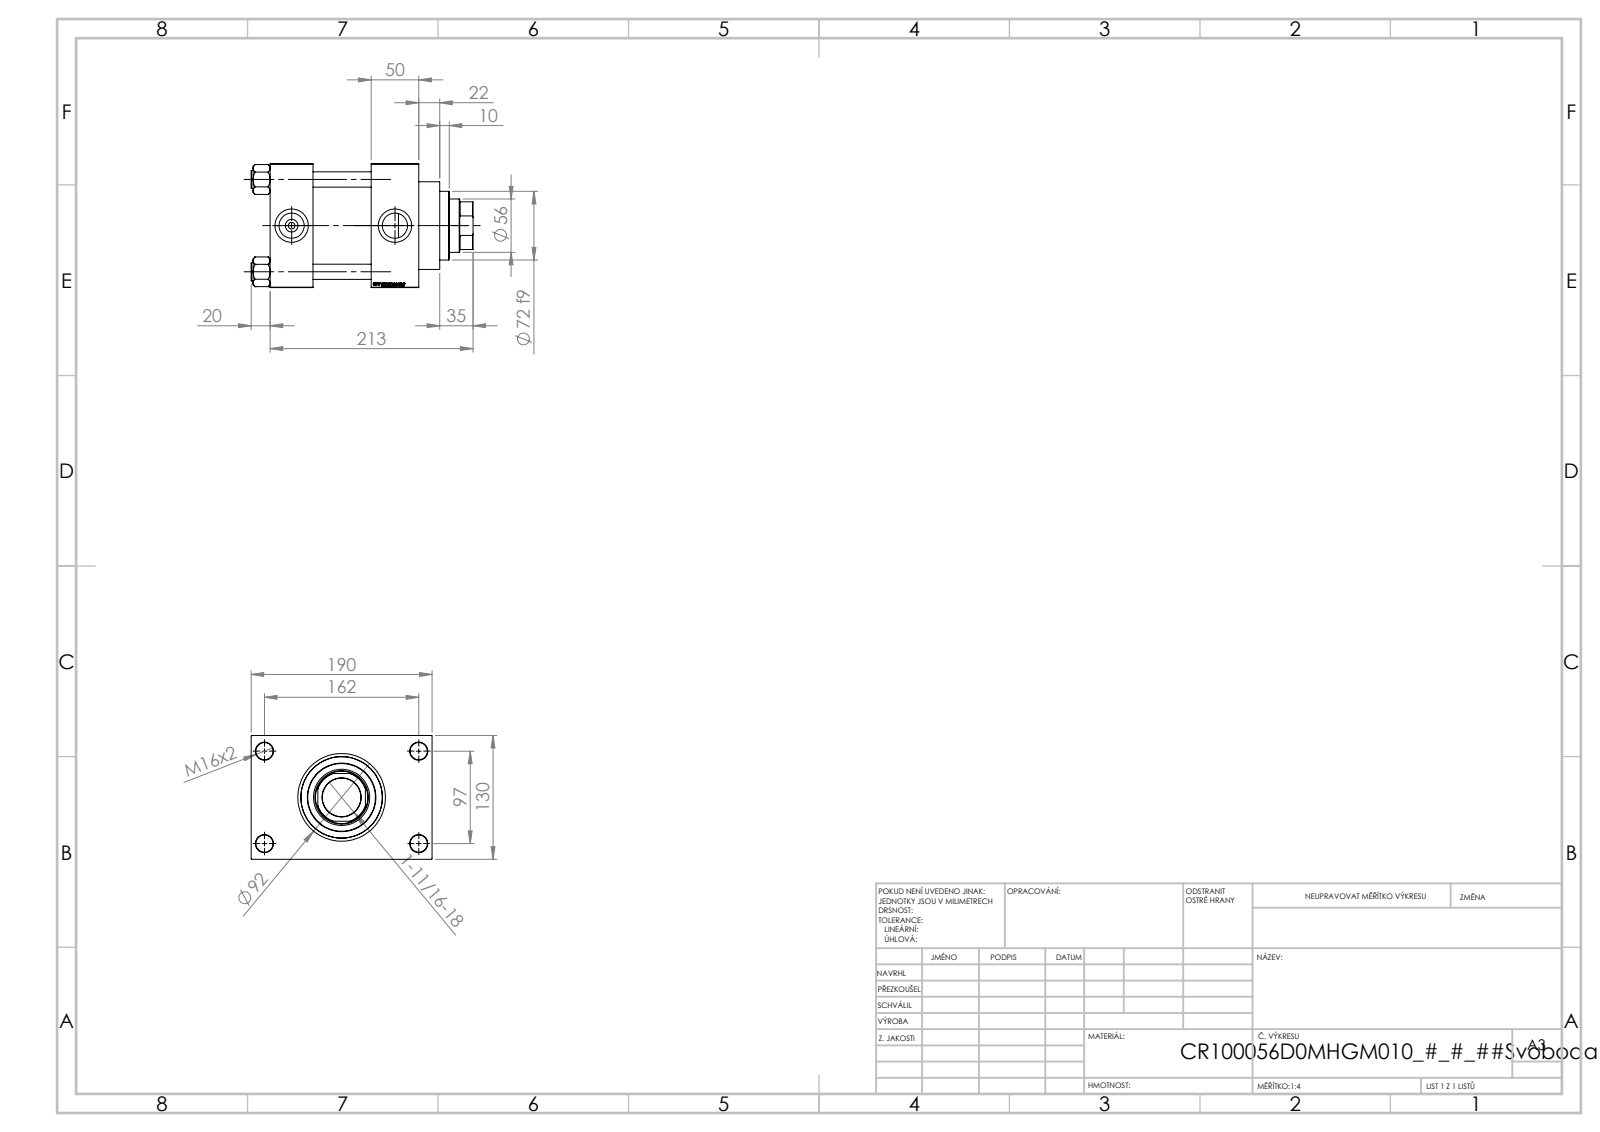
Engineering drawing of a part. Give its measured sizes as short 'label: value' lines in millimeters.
name: V215CR_D_Body; NUT_M5_D; V215CR_VCP_D; V215_VC_A (+1 more)
written by: SolidWorks 2019 (CONFIG_CONTROL_DESIGN)
unit: mm
bodies: 11 solids, 1151 faces (545 planar, 88 cylindrical, 518 other)
size: 233 × 190 × 130
volume: 2 586 000 mm³; area: 352 122 mm²
holes: 4× ⌀16, 4× ⌀18, 2× ⌀7, 2× ⌀26.44, 2× ⌀35, 1× ⌀40.5, 1× ⌀56, 1× ⌀59, 1× ⌀76, 1× ⌀85.5, 1× ⌀100
bosses: 4× ⌀19, 1× ⌀106, 1× ⌀92, 1× ⌀72
rounds: 1× R27
face distances: 130, 50, 45, 106, 61, 156, 111, 30, 160, 10
hole spacings: 32.55, 68.52, 94.41, 96.9, 102.27, 129.45, 161.73, 97
